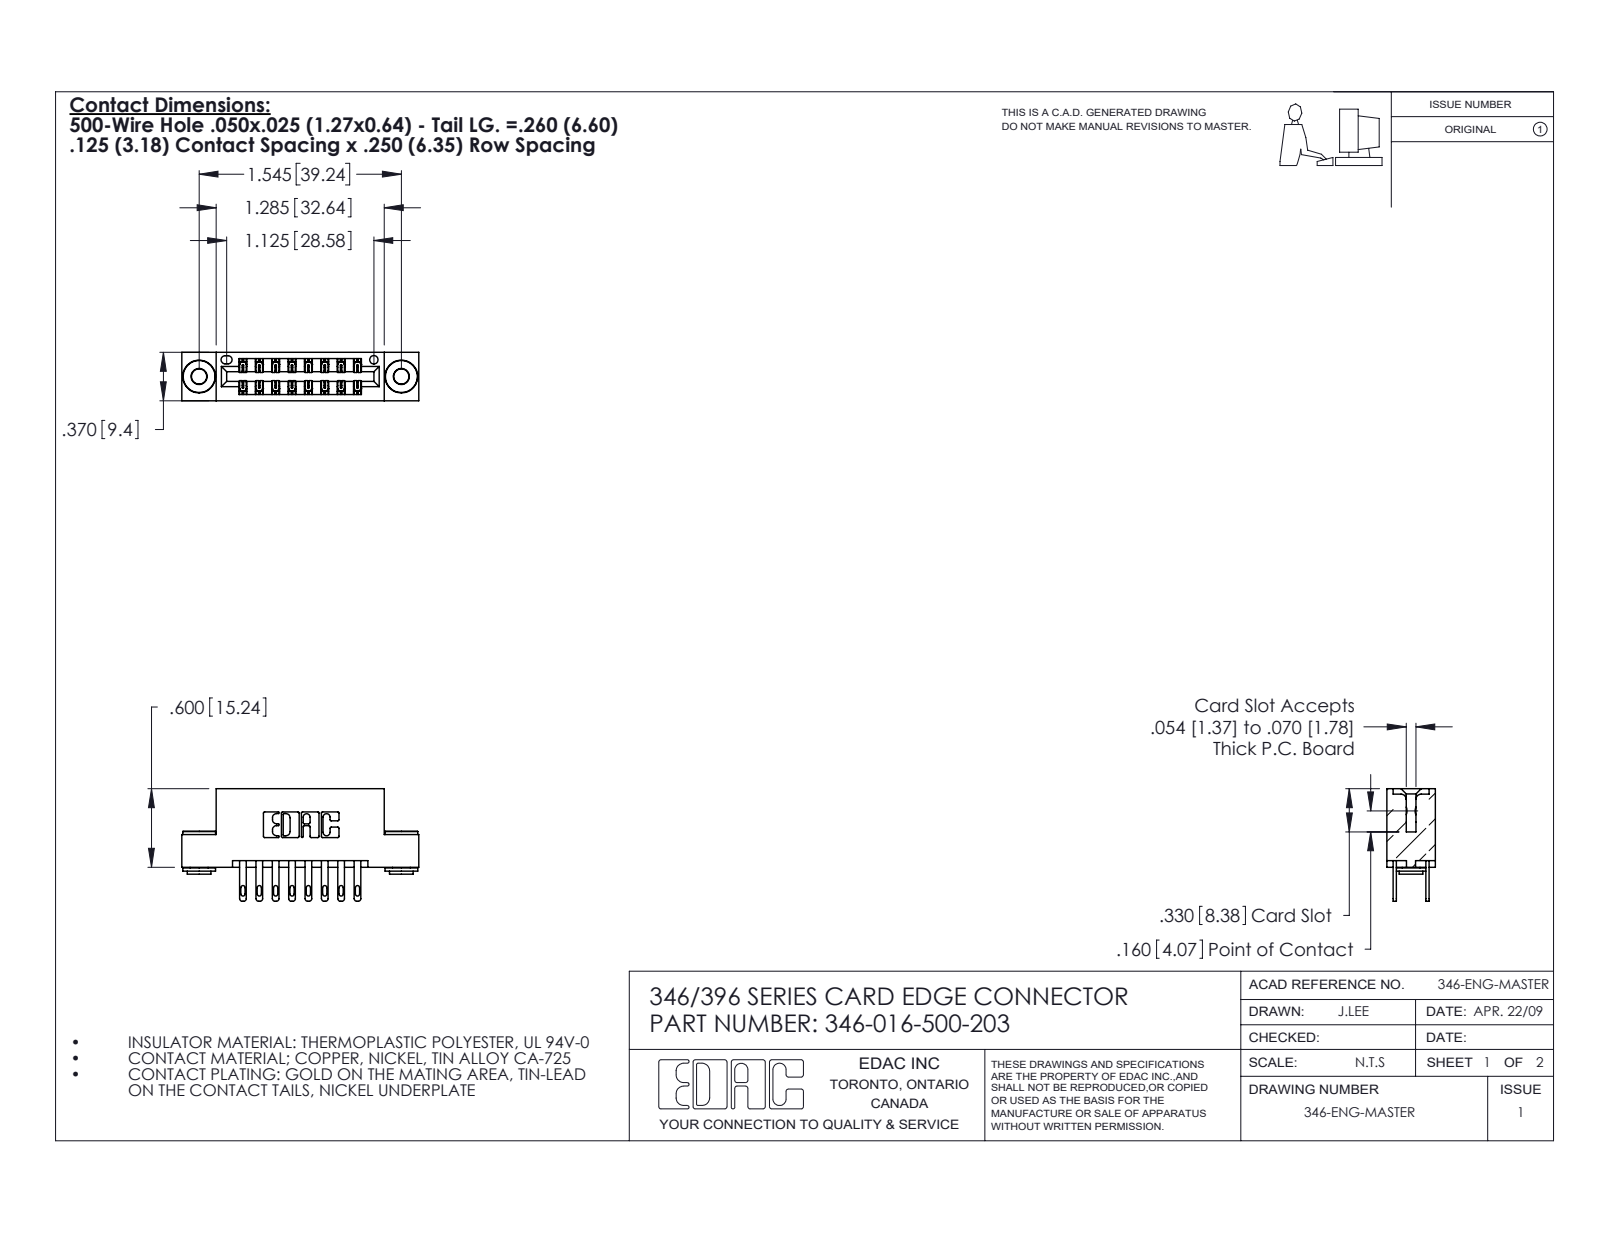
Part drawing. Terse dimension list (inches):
name: 346-016-500-203; 346 Part_Flush Mounting Lugs - 0.156 Dia-TH; 345-250-002_345-250-002-102; 345-292-001_345-293-100
written by: SolidWorks 2020 (CONFIG_CONTROL_DESIGN)
unit: in
bodies: 19 solids, 942 faces (564 planar, 370 cylindrical, 8 other)
size: 1.81 × 0.86 × 0.37
volume: 0.261 in³; area: 8.913 in²
holes: 2× ⌀0.116, 2× ⌀0.156, 1× ⌀0.064
bosses: 2× ⌀0.25, 2× ⌀0.18, 2× ⌀0.136
rounds: 24× R0.006, 22× R0.01, 16× R0.016, 16× R0.02, 6× R0.007, 6× R0.031, 3× R0.026, 2× R0.014
face distances: 0.25, 0.048, 0.322, 0.37, 0.025, 0.072, 0.298, 0.275, 0.5, 0.148
hole spacings: 0.246, 1.341, 1.545
